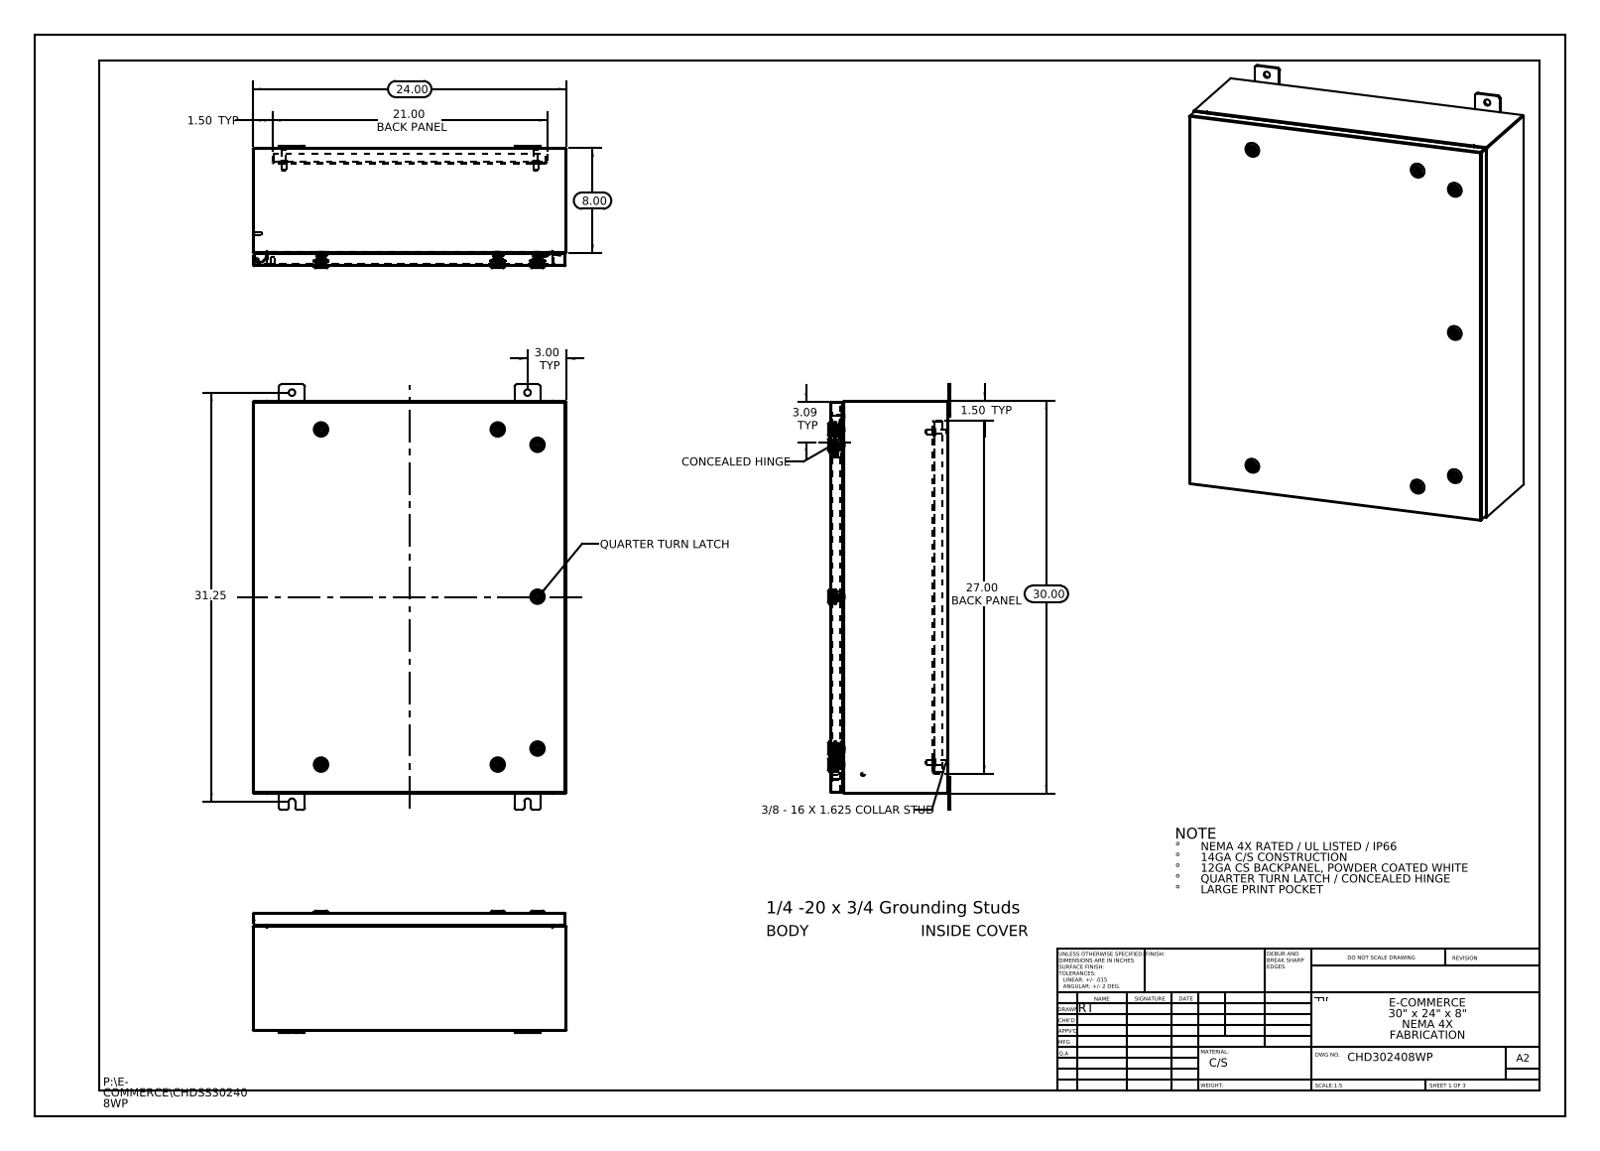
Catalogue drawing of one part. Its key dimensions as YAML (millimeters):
part_name: "Washer-221320-IB-Industrilas_Washer-221320-IB-Industrilas; CHDSS302408WP Cover; Concealed Hinge (Cover Side); Concealed Hinge enclosure side (+8 more)"
step_written_by: "SolidWorks 2013 (CONFIG_CONTROL_DESIGN)"
units: millimeters
bodies: {solids: 60, faces: 6230, planar: 1808, cylindrical: 1940, other: 2482}
overall_size: [825.5, 609.6, 237.6]
volume: 4374000
surface_area: 4271000
round_holes:
  - {diameter: 12.7, count: 8}
  - {diameter: 5, count: 7}
  - {diameter: 10, count: 7}
  - {diameter: 10.2, count: 7}
  - {diameter: 16, count: 7}
  - {diameter: 20, count: 7}
  - {diameter: 3.5, count: 4}
  - {diameter: 5.4, count: 1}
round_bosses_or_shafts:
  - {diameter: 6, count: 9}
  - {diameter: 28, count: 7}
  - {diameter: 19.8, count: 7}
  - {diameter: 15.9, count: 7}
  - {diameter: 15.5, count: 7}
  - {diameter: 13.5, count: 7}
  - {diameter: 10, count: 7}
  - {diameter: 2.9, count: 7}
partial_cylinders:
  - {radius: 0.2, count: 231}
  - {radius: 3, count: 231}
  - {radius: 0.7, count: 84}
  - {radius: 0.5, count: 28}
  - {radius: 5, count: 28}
  - {radius: 4.8, count: 24}
  - {radius: 0.3, count: 22}
  - {radius: 2.2, count: 18}
face_to_face_distances: [1.9, 1.9, 228.9, 226.9, 227, 225.1, 2.6, 25.4, 27.3, 199.7]
hole_center_spacings: [47.2, 294.6, 342.9, 457.2, 489, 641.4, 650.2, 686]
